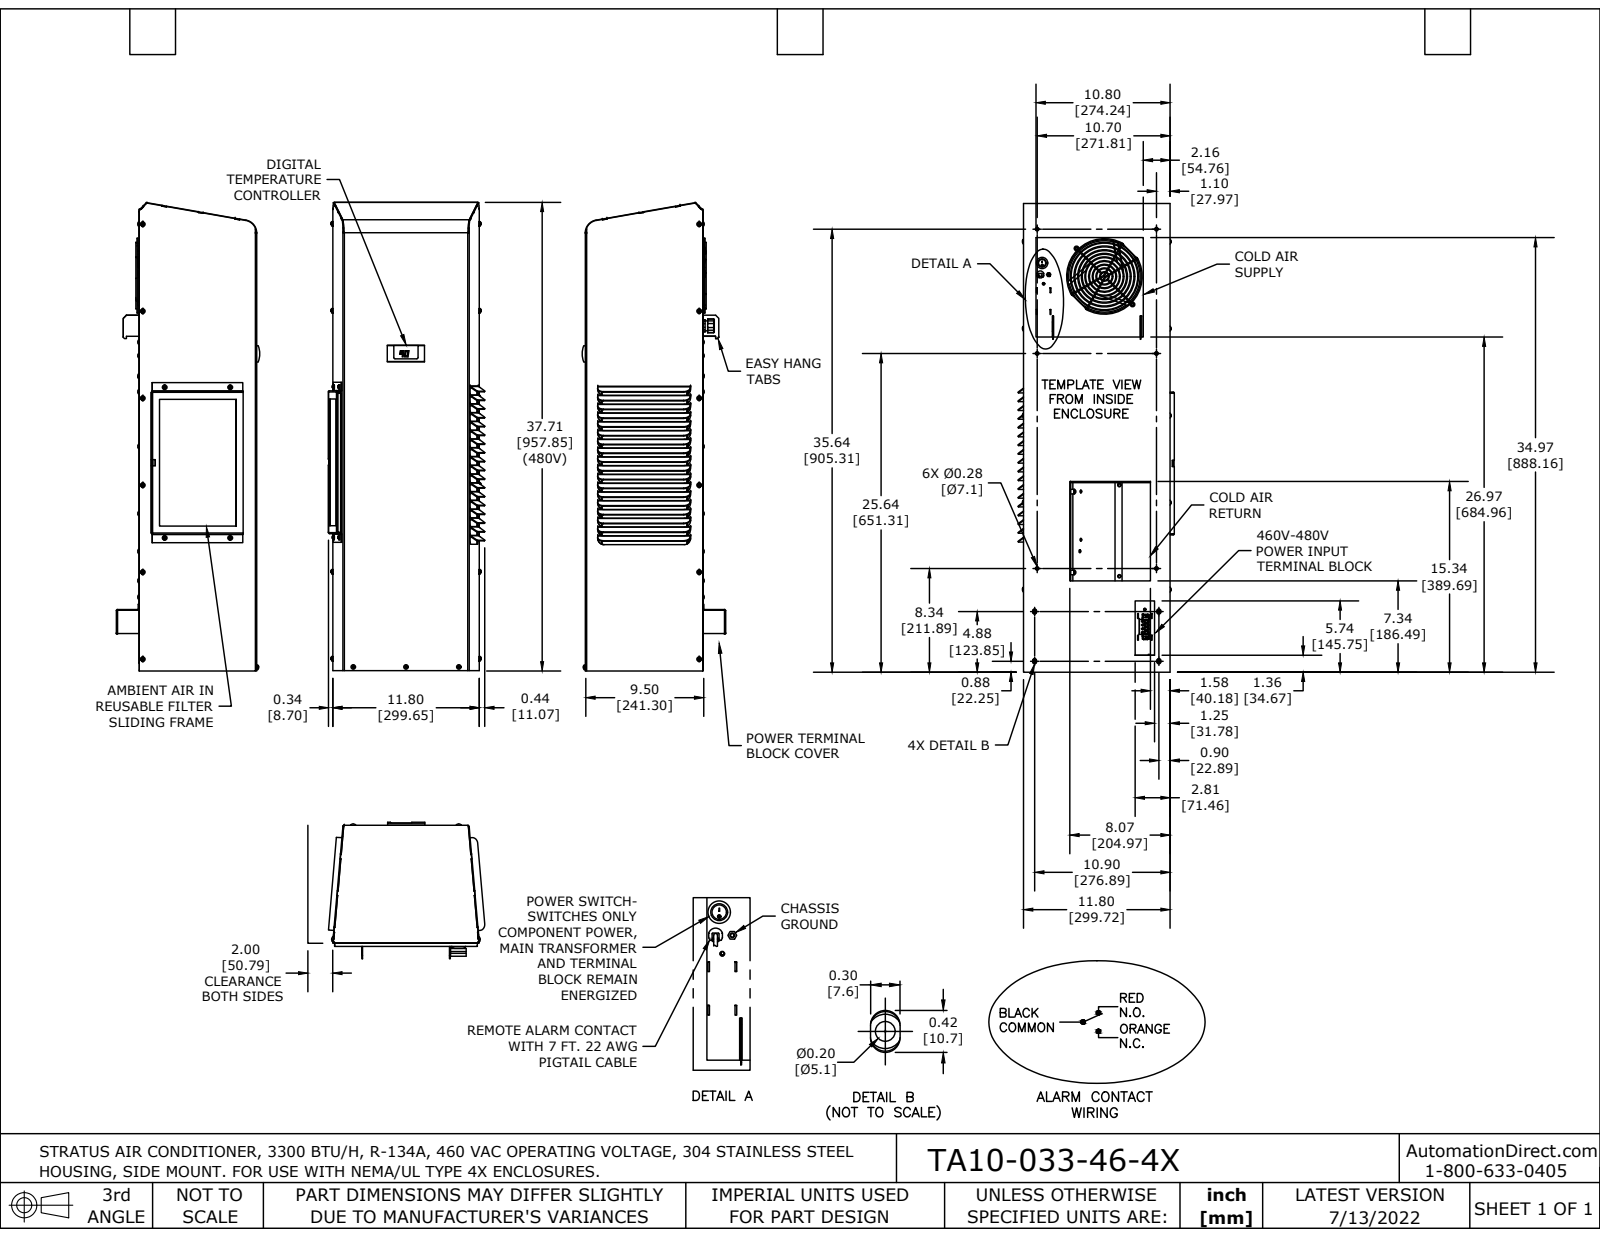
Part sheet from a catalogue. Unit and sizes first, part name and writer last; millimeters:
Units: millimetres
Overall size (bounding box): 813.4 × 319.4 × 293.3
Round holes (diameter × count): ⌀4 ×11, ⌀5.2 ×5, ⌀152.4 ×1
Round bosses / shafts (diameter × count): ⌀4.8 ×7, ⌀9 ×2, ⌀6.3 ×2, ⌀154.2 ×1, ⌀23 ×1, ⌀9.8 ×1, ⌀9.6 ×1, ⌀2.2 ×1
Partial cylindrical surfaces — rounded edges, fillets, slot ends (radius × count): R0.4 ×45, R0.3 ×42, R12.7 ×36, R12.9 ×36, R2.5 ×28, R1.5 ×21, R2.9 ×21, R0.8 ×13
Main face-to-face distances: 1.5, 239.6, 238.2, 1.5, 241.1, 2.3, 6.4, 7.8, 246, 247.5
Hole centre spacings: 177.8, 355.6, 533.4, 44, 134.6, 166.8, 276.1, 307.8
Volume: 2 237 000 mm³ · Surface area: 2 063 000 mm²
Bodies: 1 solid, 1743 faces (1077 planar, 496 cylindrical, 170 other)
Part name (STEP PRODUCT): TA10-033-46-4X
STEP written by: SolidWorks 2021 (AUTOMOTIVE_DESIGN)
